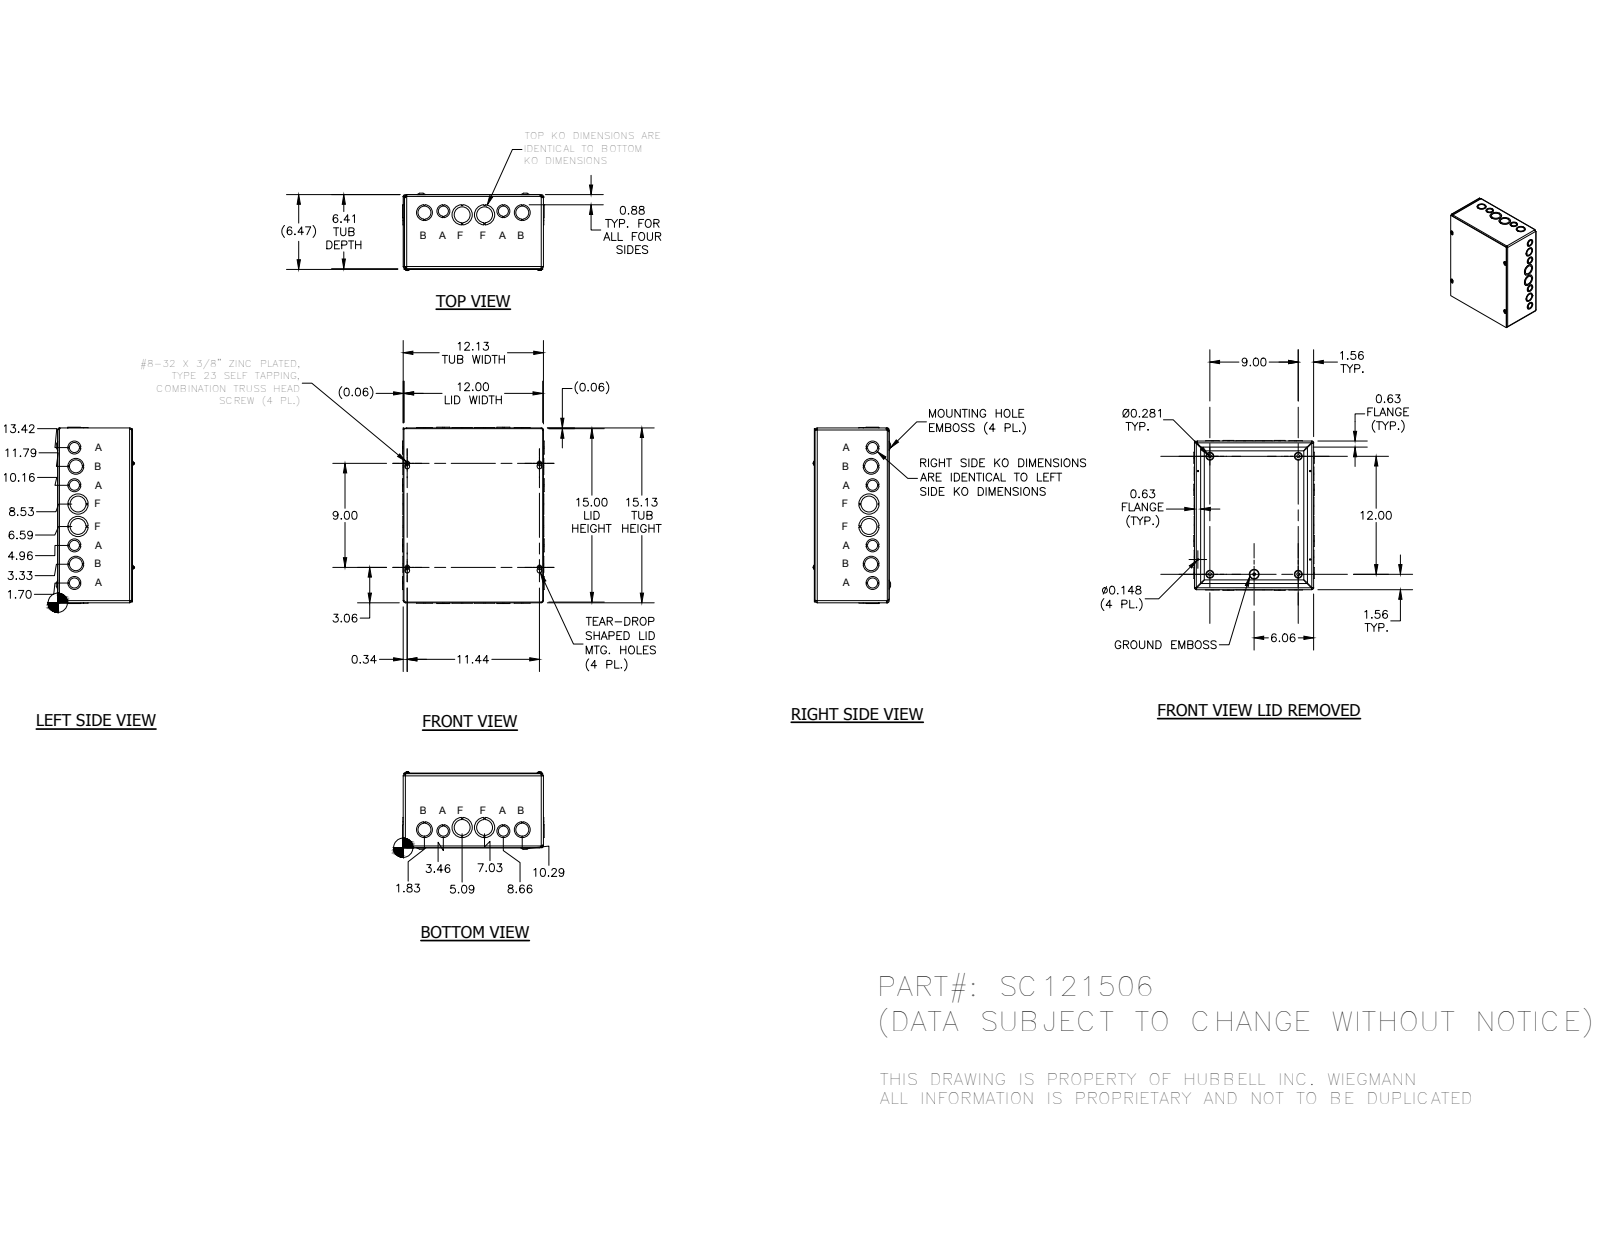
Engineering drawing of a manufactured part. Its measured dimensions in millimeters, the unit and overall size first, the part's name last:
Units: millimetres
Overall size (bounding box): 387.32 × 311.12 × 170
Round holes (diameter × count): ⌀28.57 ×10, ⌀34.92 ×8, ⌀22.22 ×6, ⌀3.76 ×4, ⌀7.62 ×4, ⌀44.45 ×4, ⌀4.19 ×1
Round bosses / shafts (diameter × count): ⌀9.75 ×4, ⌀4.17 ×4, ⌀5.8 ×1
Partial cylindrical surfaces — rounded edges, fillets, slot ends (radius × count): R3.17 ×12, R4.75 ×8, R1.4 ×4, R1.57 ×4, R2.38 ×4, R2.97 ×4, R3.15 ×4, R3.96 ×4
Main face-to-face distances: 1.57, 161.12, 1.58, 162.69, 1.59, 162.71, 164.28, 307.98, 306.4, 306.41
Hole centre spacings: 41.52, 42.15, 49.09, 82.94, 91.03, 132.17, 173.51, 228.6
Bodies: 30 solids, 1142 faces (749 planar, 235 cylindrical, 158 other)
Part name (STEP PRODUCT): SC1215BKP; SC121506WRA; SC1215LID; 34056 (+1 more)
STEP written by: Autodesk Inventor 2014 (AUTOMOTIVE_DESIGN)
